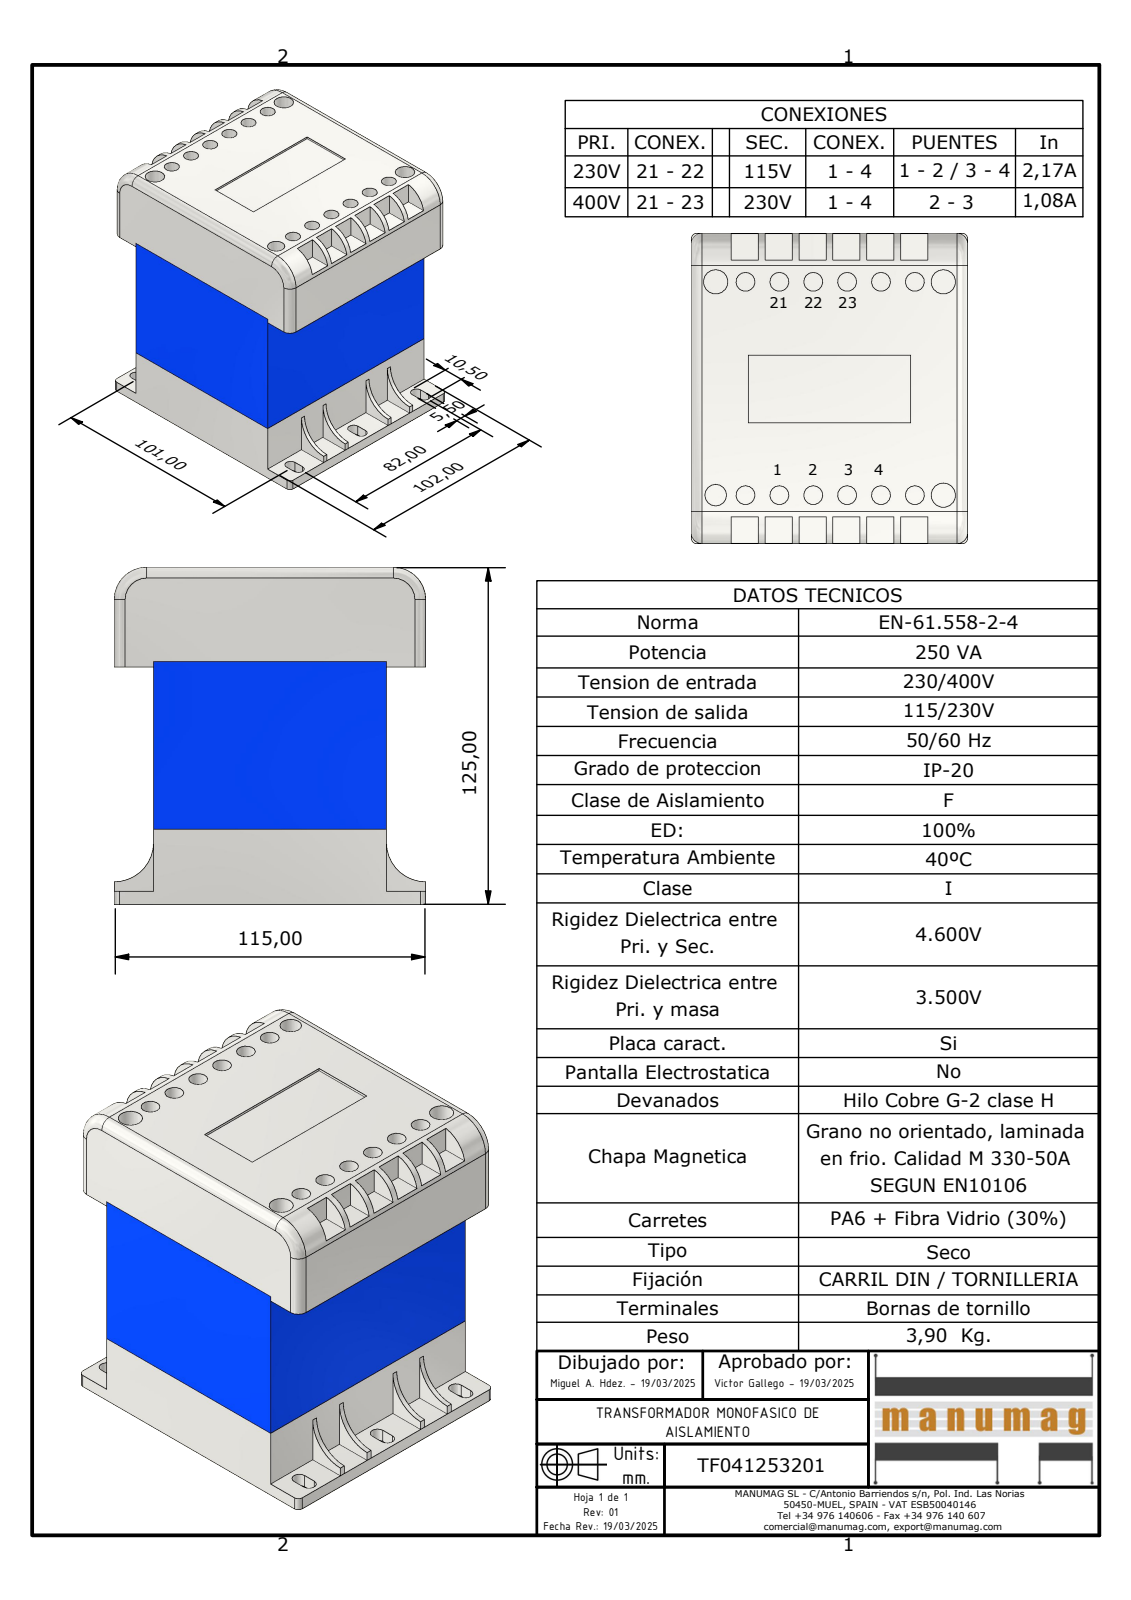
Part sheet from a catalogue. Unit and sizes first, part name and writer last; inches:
Units: inches
Overall size (bounding box): 4.921 × 4.528 × 4.016
Round holes (diameter × count): ⌀0.276 ×12, ⌀0.354 ×3, ⌀0.315 ×1
Partial cylindrical surfaces — rounded edges, fillets, slot ends (radius × count): R0.098 ×8, R0.157 ×6, R0.079 ×4, R0.472 ×2, R0.571 ×2
Main face-to-face distances: 0.039, 3.346, 3.976, 0.197, 4.016, 3.543, 3.386, 3.307, 3.937, 1.378
Hole centre spacings: 0.492, 3.149, 0.984, 3.11, 3.262, 1.476, 3.443, 1.969
Volume: 29.47 in³ · Surface area: 211 in²
Bodies: 11 solids, 200 faces (152 planar, 44 cylindrical, 4 other)
Part name (STEP PRODUCT): TF041253201; INFERIOR EI96; CENTRAL EI96-60; SUPERIOR EI96
STEP written by: Autodesk Inventor 2023 (AUTOMOTIVE_DESIGN)
